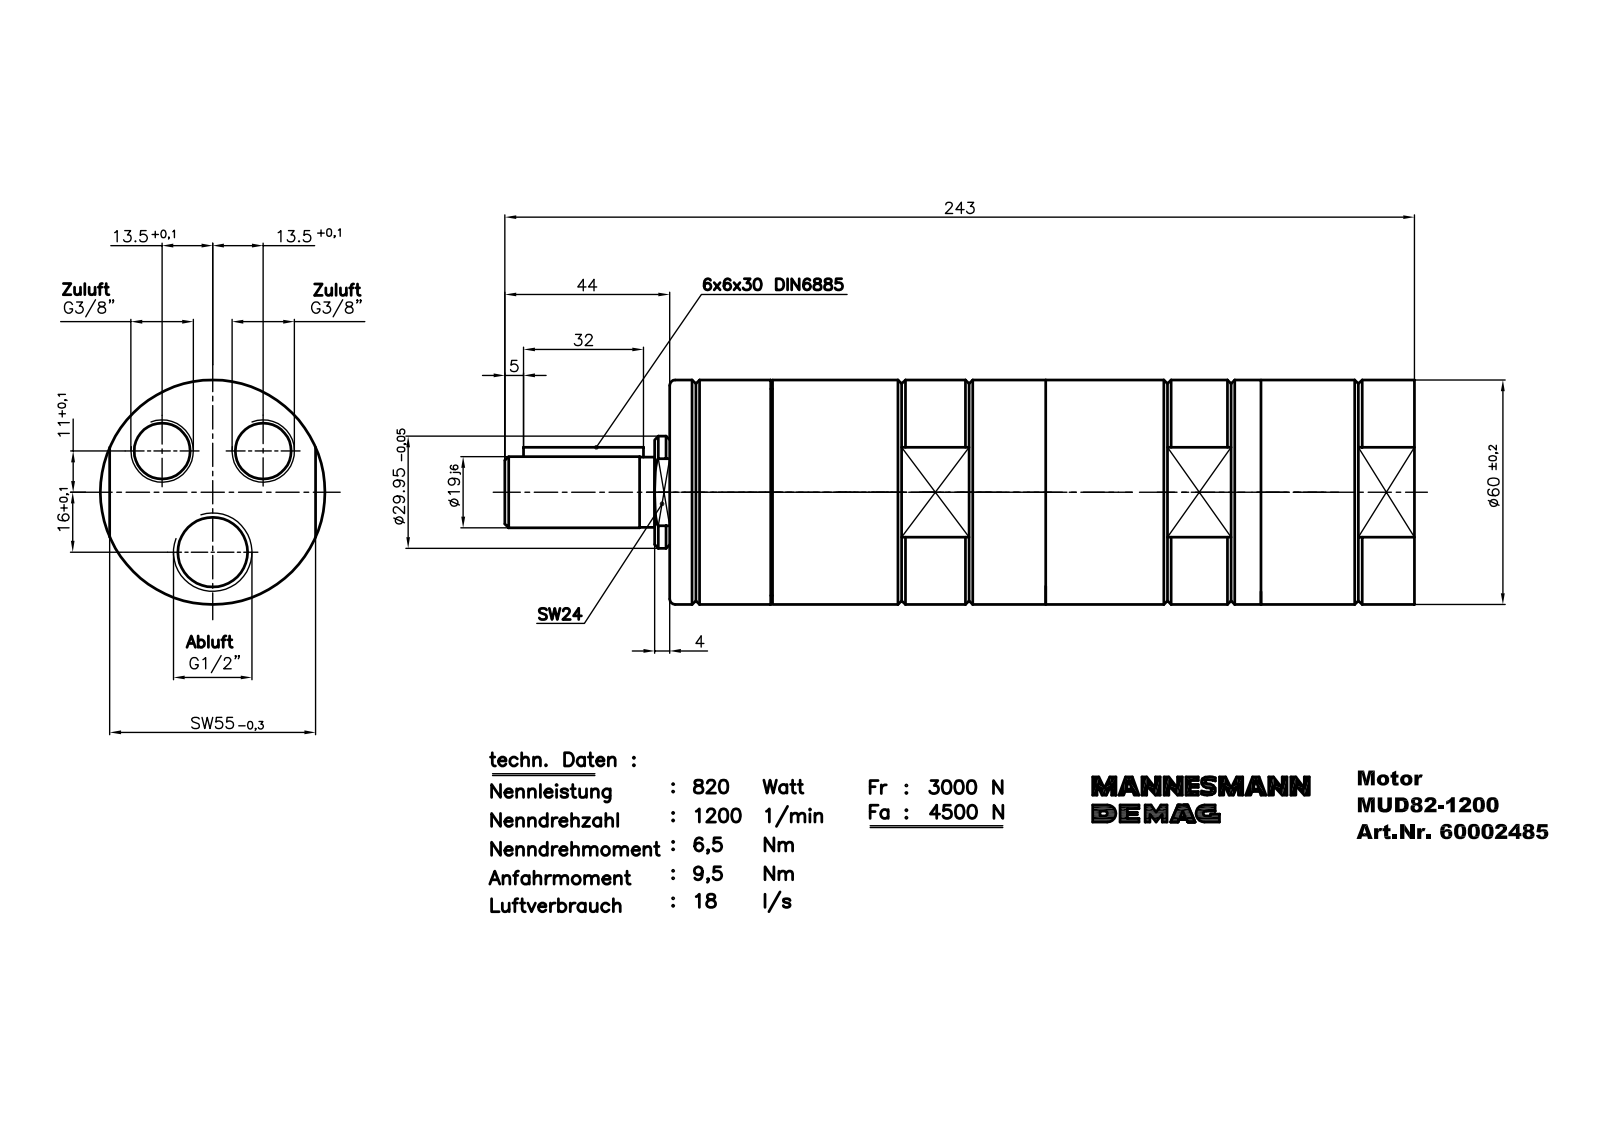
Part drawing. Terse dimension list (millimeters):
name: MUD 82-1200_60002485
written by: Autodesk Inventor 2008 (CONFIG_CONTROL_DESIGN)
unit: mm
bodies: 1 solid, 185 faces (104 planar, 36 cylindrical, 45 other)
size: 243 × 60 × 60
volume: 558 523 mm³; area: 51 256 mm²
holes: 1× ⌀1.55, 1× ⌀4, 1× ⌀5.5, 1× ⌀35
bosses: 1× ⌀60, 1× ⌀57.96, 1× ⌀29.95, 1× ⌀19, 1× ⌀18.8, 1× ⌀5, 1× ⌀3.6
rounds: 2× R3, 2× R7.5, 1× R8.5, 1× R23.5, 1× R27.16
face distances: 199, 55, 182.26, 16.74, 186, 3.74, 13, 4, 186.26, 190
